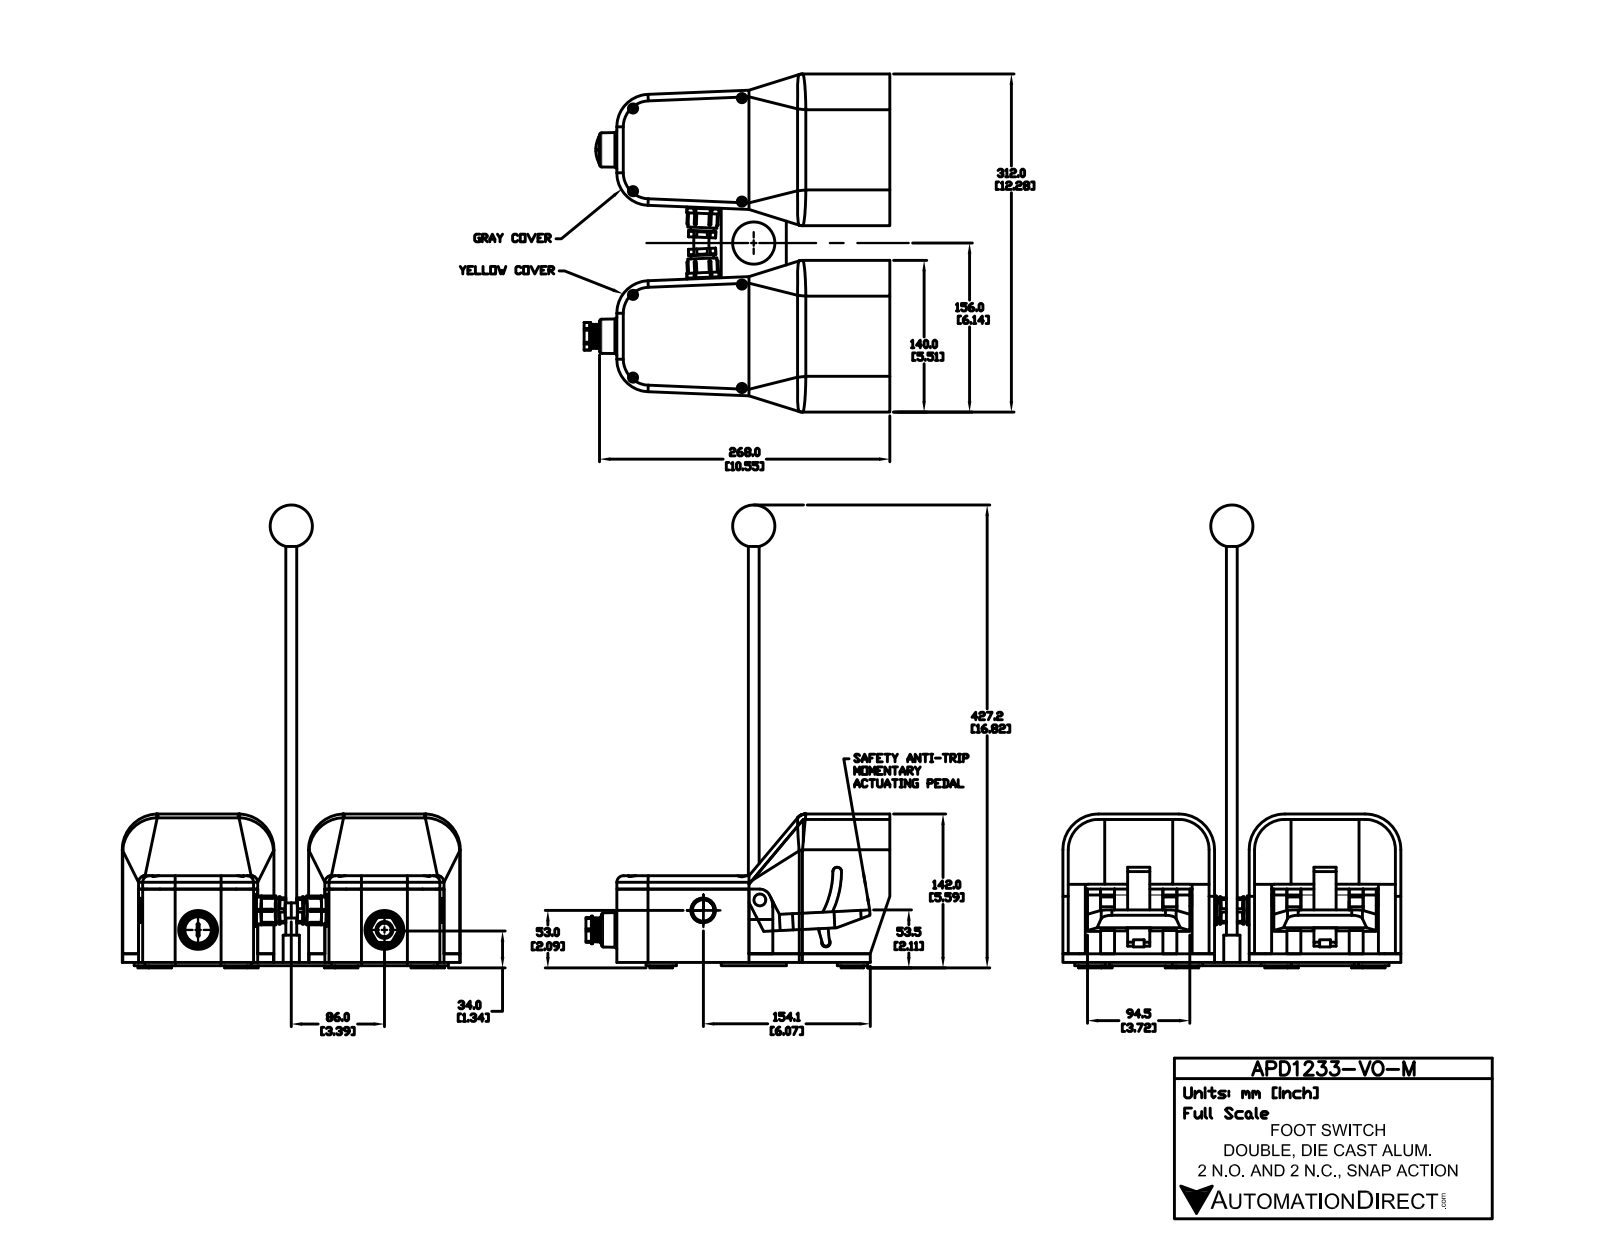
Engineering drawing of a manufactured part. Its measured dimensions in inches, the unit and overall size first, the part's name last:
Units: inches
Overall size (bounding box): 16.817 × 12.283 × 11.112
Round holes (diameter × count): ⌀0.335 ×8, ⌀0.896 ×4, ⌀0.498 ×1, ⌀0.614 ×1
Round bosses / shafts (diameter × count): ⌀1.102 ×8, ⌀0.827 ×8, ⌀0.782 ×4, ⌀1.171 ×2, ⌀1.051 ×2, ⌀0.992 ×2, ⌀0.846 ×2, ⌀1.004 ×1
Partial cylindrical surfaces — rounded edges, fillets, slot ends (radius × count): R0.039 ×34, R0.042 ×12, R0.394 ×11, R0.236 ×5, R1.102 ×4, R1.181 ×4, R1.299 ×4, R0.787 ×2
Main face-to-face distances: 0.197, 5.315, 6.772, 0.315, 2.348, 5.512, 2.664, 2.349, 2.663, 0.118
Hole centre spacings: 3.976, 5.206, 6.772, 3.004, 3.76, 5.211, 7.52, 8.172
Volume: 197.7 in³ · Surface area: 906.5 in²
Bodies: 38 solids, 865 faces (514 planar, 237 cylindrical, 114 other)
Part name (STEP PRODUCT): APD1233-V0-M
STEP written by: SolidWorks 2015 (AUTOMOTIVE_DESIGN)
